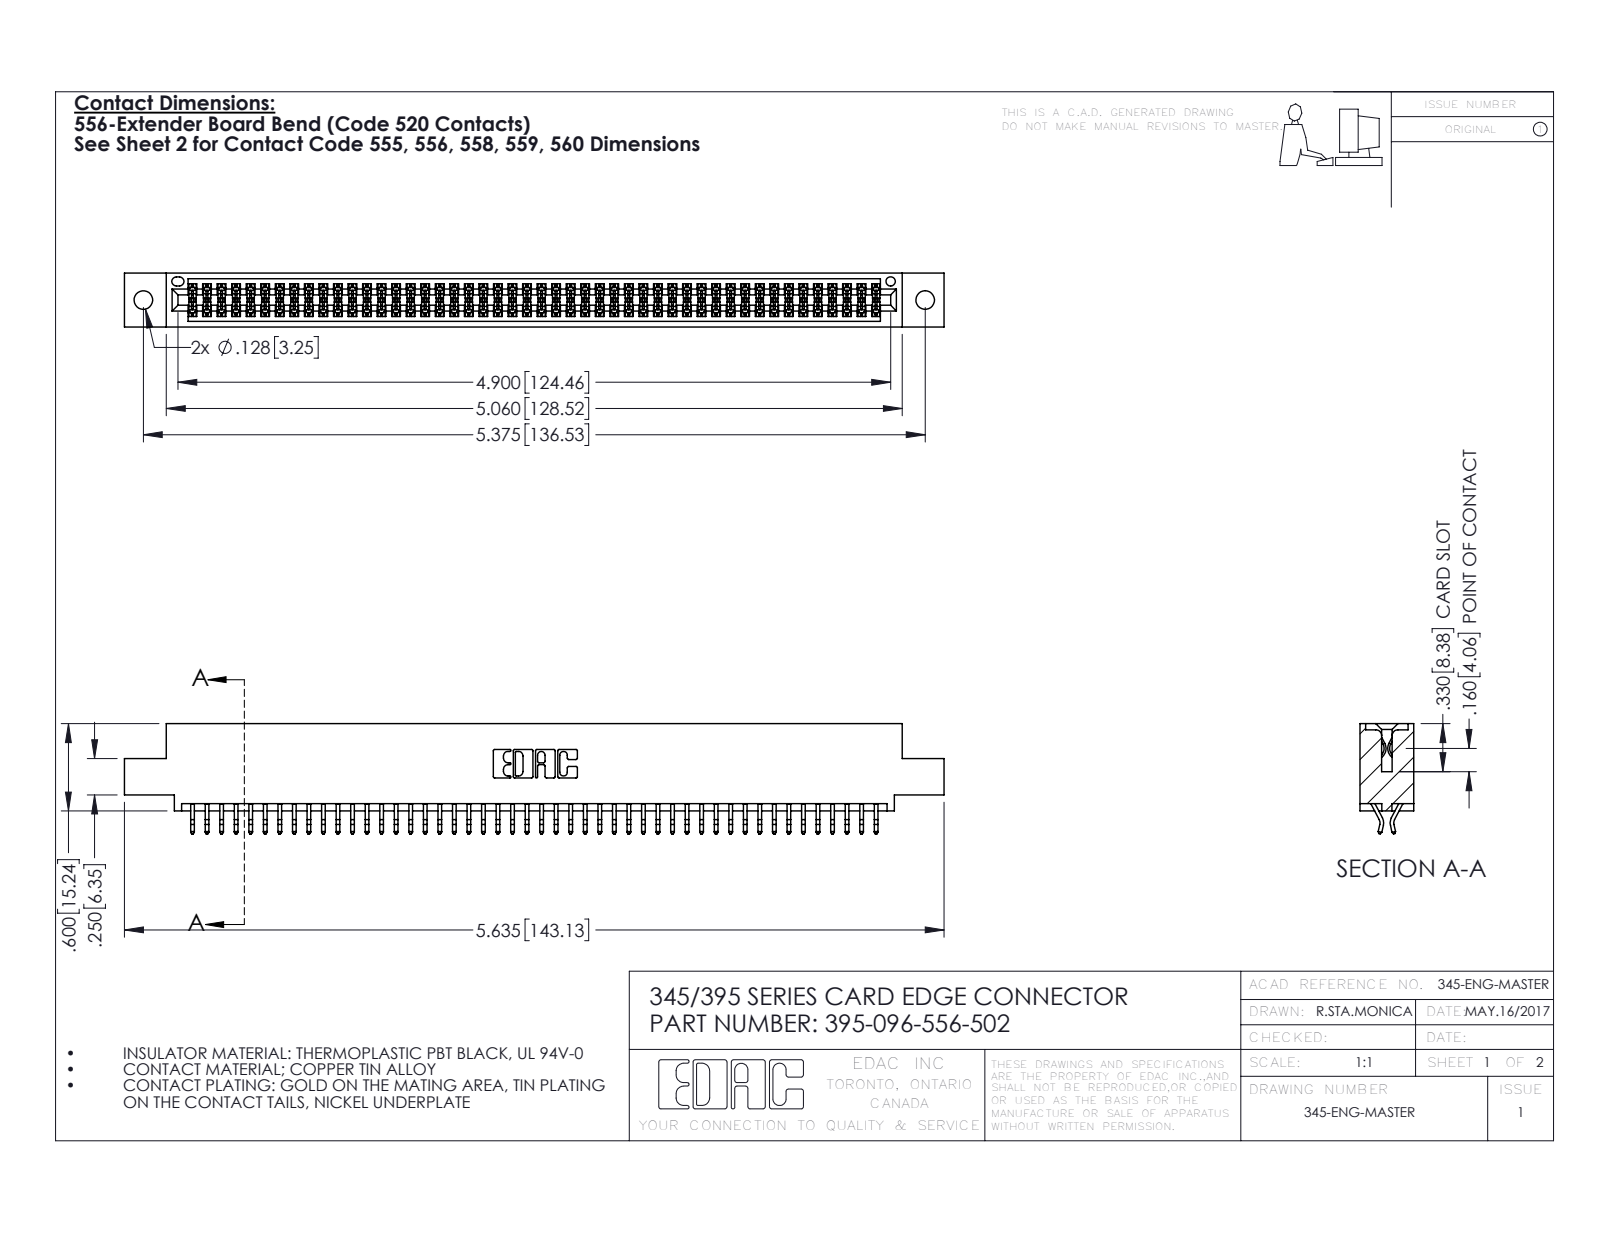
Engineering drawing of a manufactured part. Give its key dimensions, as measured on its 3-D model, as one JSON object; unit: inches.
{"part_name": "395-096-556-502; 345-292-001_556 Tail; 345 Part_0.110 Offset - 0.128 Dia", "step_written_by": "SolidWorks 2016 (CONFIG_CONTROL_DESIGN)", "units": "inches", "bodies": {"solids": 97, "faces": 5506, "planar": 3636, "cylindrical": 1870, "other": 0}, "overall_size": [5.635, 0.757, 0.37], "volume_in3": 0.845, "surface_area_in2": 31.49, "round_holes": [[0.128, 2], [0.064, 1]], "partial_cylinders_radius": [[0.006, 144], [0.01, 22], [0.007, 6], [0.031, 6], [0.026, 3], [0.01, 2], [0.014, 2], [0.019, 2]], "face_to_face_distances": [0.298, 0.072, 0.37, 0.2, 0.025, 0.098, 0.272, 0.225, 0.175, 0.149], "hole_center_spacings": [0.27, 5.139, 5.375]}
